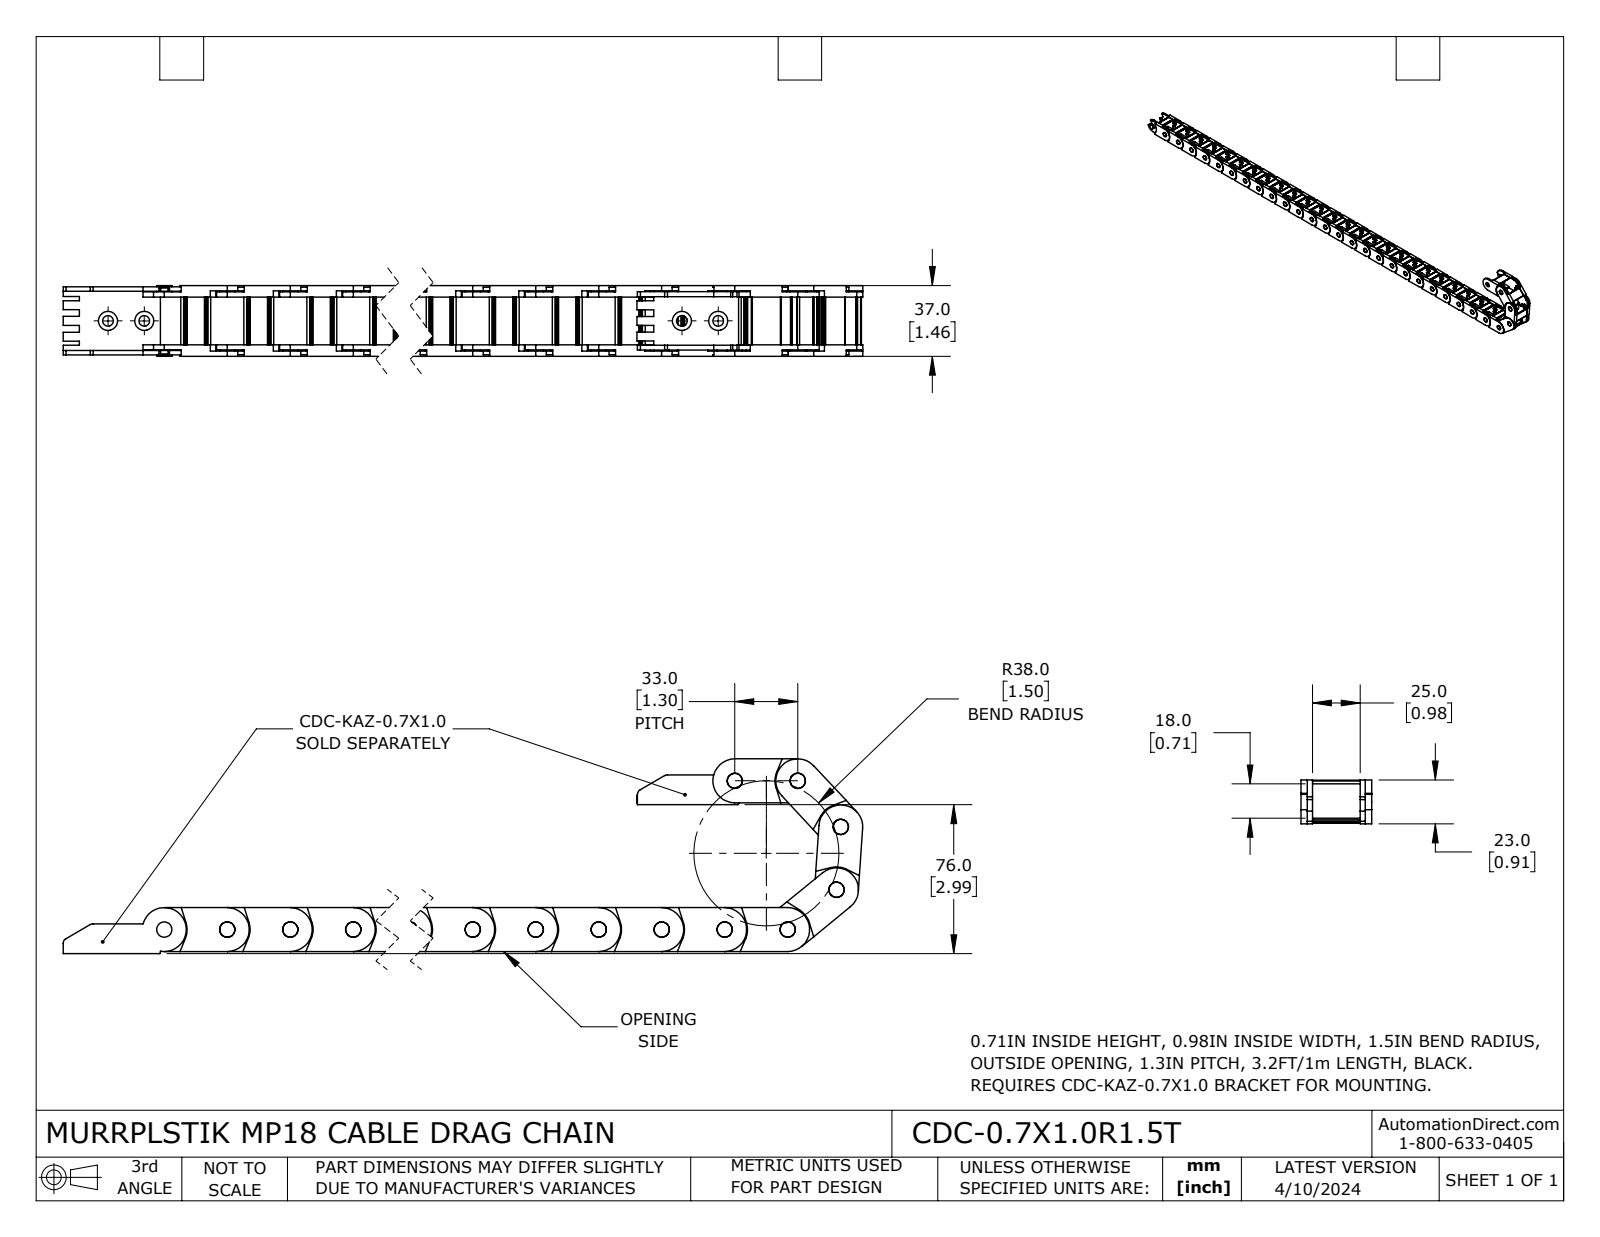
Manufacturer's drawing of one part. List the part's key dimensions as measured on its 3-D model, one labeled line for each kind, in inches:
Part name (STEP PRODUCT): CDC-0.7X1.0R1.5T
STEP written by: SolidWorks 2023 (CONFIG_CONTROL_DESIGN)
Units: inches
Bodies: 30 solids, 2490 faces (1290 planar, 1200 cylindrical, 0 other)
Overall size (bounding box): 35.767 × 3.972 × 1.457
Volume: 16.69 in³ · Surface area: 339.5 in²
Round holes (diameter × count): ⌀0.315 ×30
Round bosses / shafts (diameter × count): ⌀0.315 ×1
Partial cylindrical surfaces — rounded edges, fillets, slot ends (radius × count): R0.02 ×120, R0.059 ×120, R0.008 ×60, R0.012 ×60, R0.453 ×31, R0.47 ×31, R0.197 ×30, R0.215 ×30
Main face-to-face distances: 1.22, 0.106, 0.13, 0.236, 1.457, 1.327, 1.091, 0.984, 1.35, 0.024
Hole centre spacings: 1.299, 2.598, 3.898, 5.197, 6.496, 7.795, 9.094, 10.394
